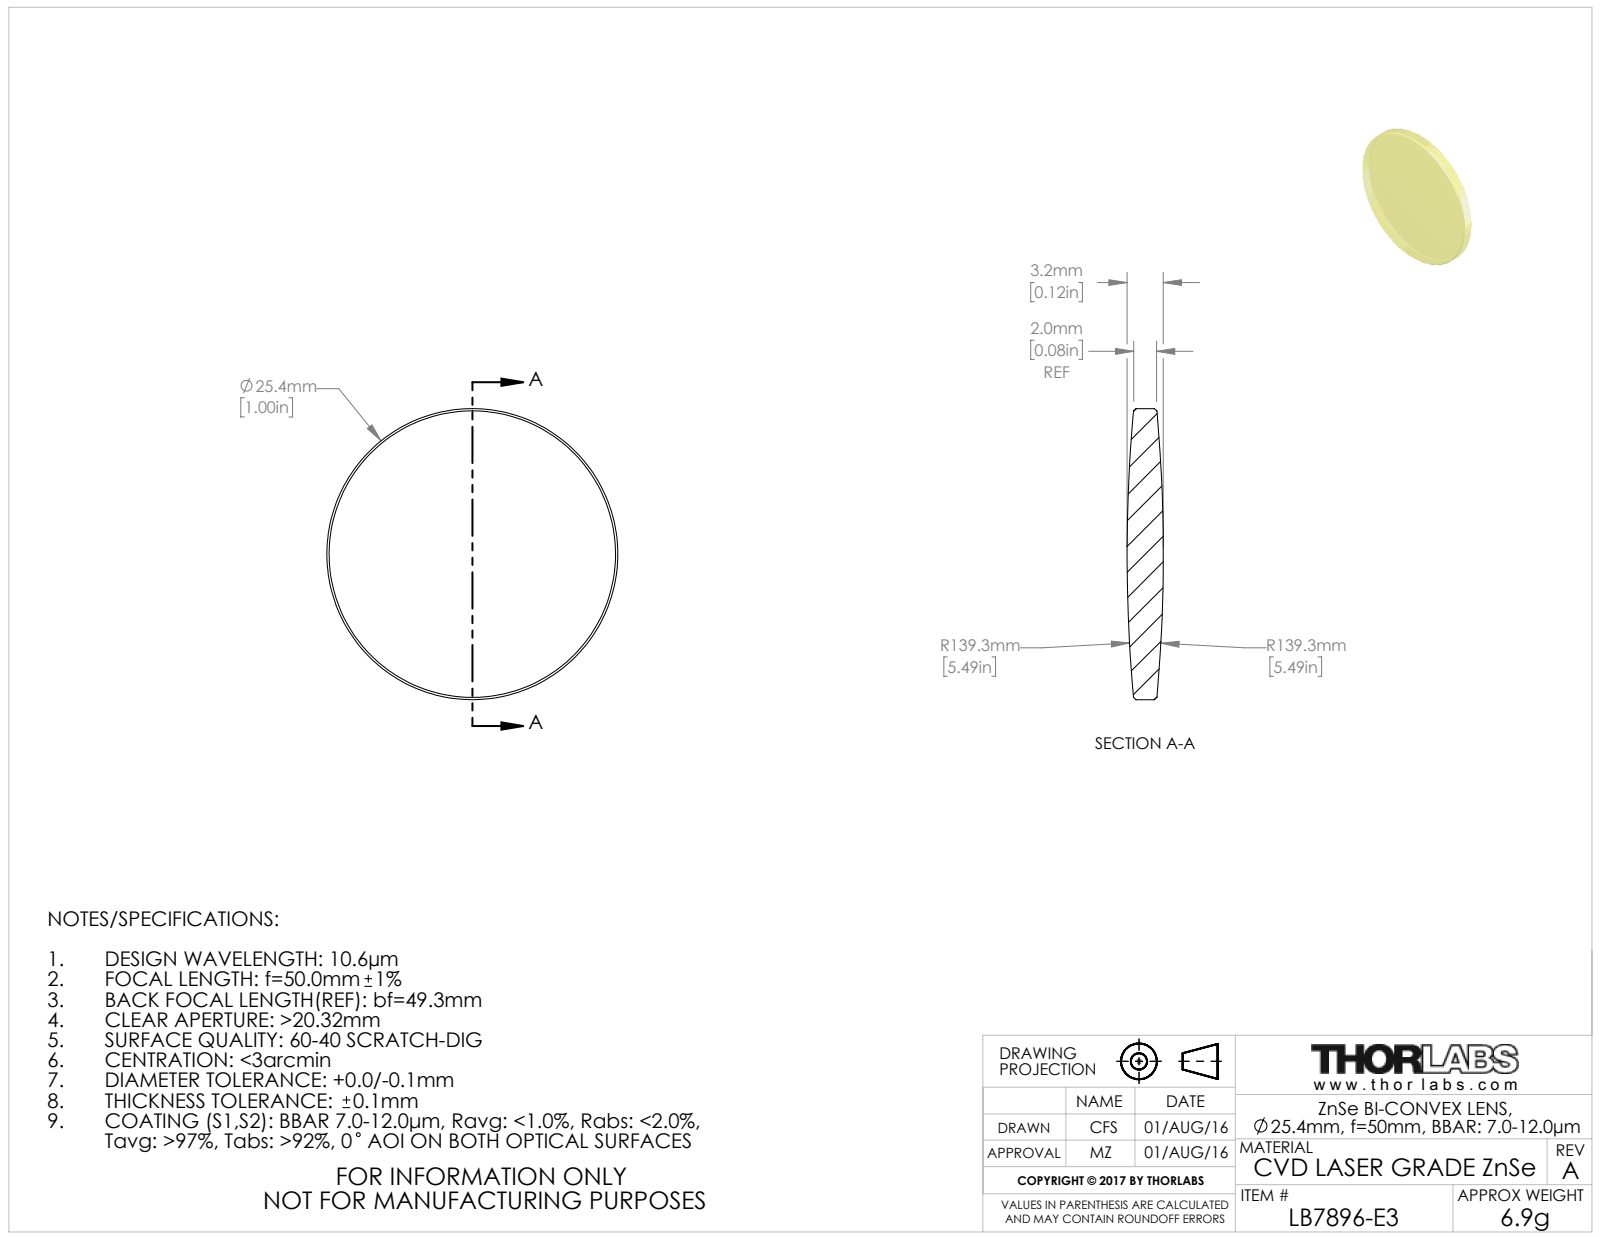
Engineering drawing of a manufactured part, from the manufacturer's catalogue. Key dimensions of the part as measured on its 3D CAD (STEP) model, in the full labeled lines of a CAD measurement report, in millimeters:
Part name (STEP PRODUCT): TTN051887-E0W
STEP written by: SolidWorks 2016 (CONFIG_CONTROL_DESIGN)
Units: millimetres
Bodies: 1 solid, 10 faces (0 planar, 2 cylindrical, 8 other)
Overall size (bounding box): 25.4 × 25.4 × 3.1
Volume: 1 300 mm³ · Surface area: 1 158 mm²
Round bosses / shafts (diameter × count): ⌀25.4 ×1
